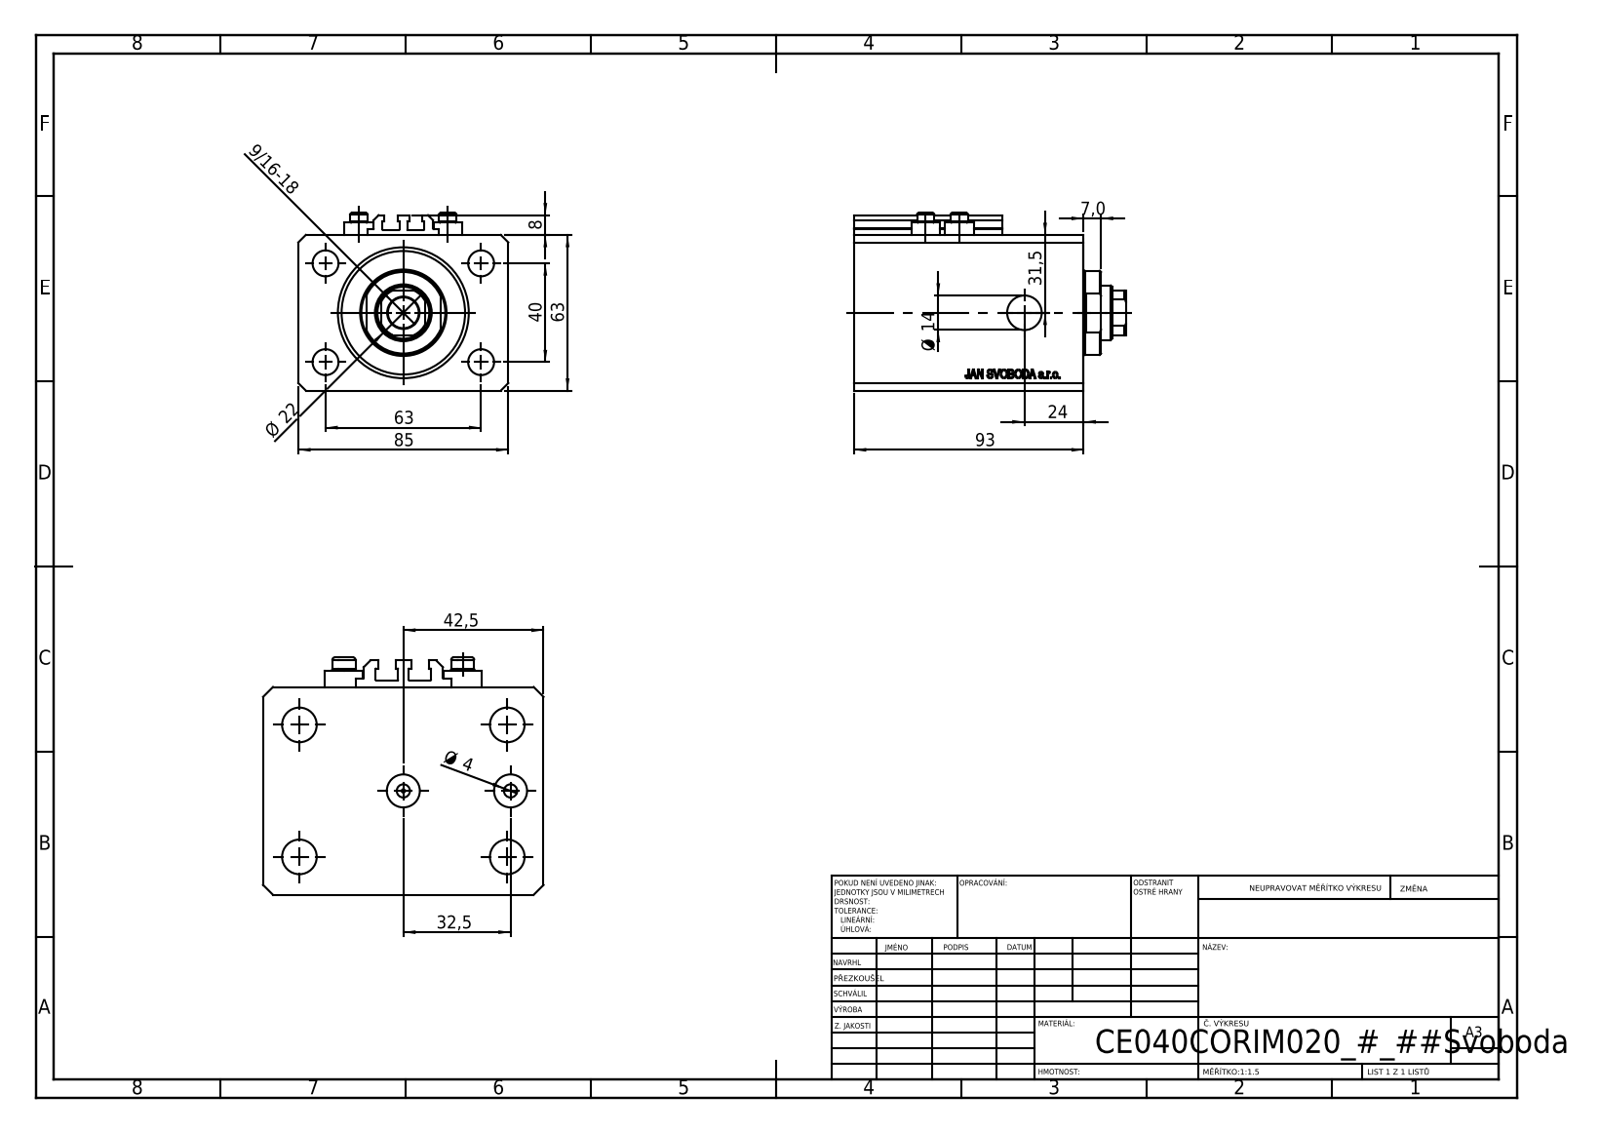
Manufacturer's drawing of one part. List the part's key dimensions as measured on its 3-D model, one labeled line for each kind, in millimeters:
Part name (STEP PRODUCT): ALLEN BOLT V250CE; V250CE_C_Body; V250CE_VC_C; V250CE_C_VCP
STEP written by: SolidWorks 2019 (CONFIG_CONTROL_DESIGN)
Units: millimetres
Bodies: 8 solids, 1036 faces (504 planar, 86 cylindrical, 446 other)
Overall size (bounding box): 110 × 85 × 72
Volume: 459 881 mm³ · Surface area: 92 481 mm²
Round holes (diameter × count): ⌀4 ×7, ⌀10.5 ×4, ⌀10 ×2, ⌀14 ×2, ⌀1.25 ×1, ⌀12.5 ×1, ⌀22 ×1, ⌀40 ×1, ⌀53 ×1
Round bosses / shafts (diameter × count): ⌀11.6 ×4, ⌀7 ×4, ⌀34 ×1
Partial cylindrical surfaces — rounded edges, fillets, slot ends (radius × count): R0.2 ×10, R10.5 ×1
Main face-to-face distances: 63, 85, 93, 17, 76, 11.4, 64.6, 81.6, 3, 10
Hole centre spacings: 37.31, 13.6, 20.02, 36, 38.48, 40, 63, 67.05
